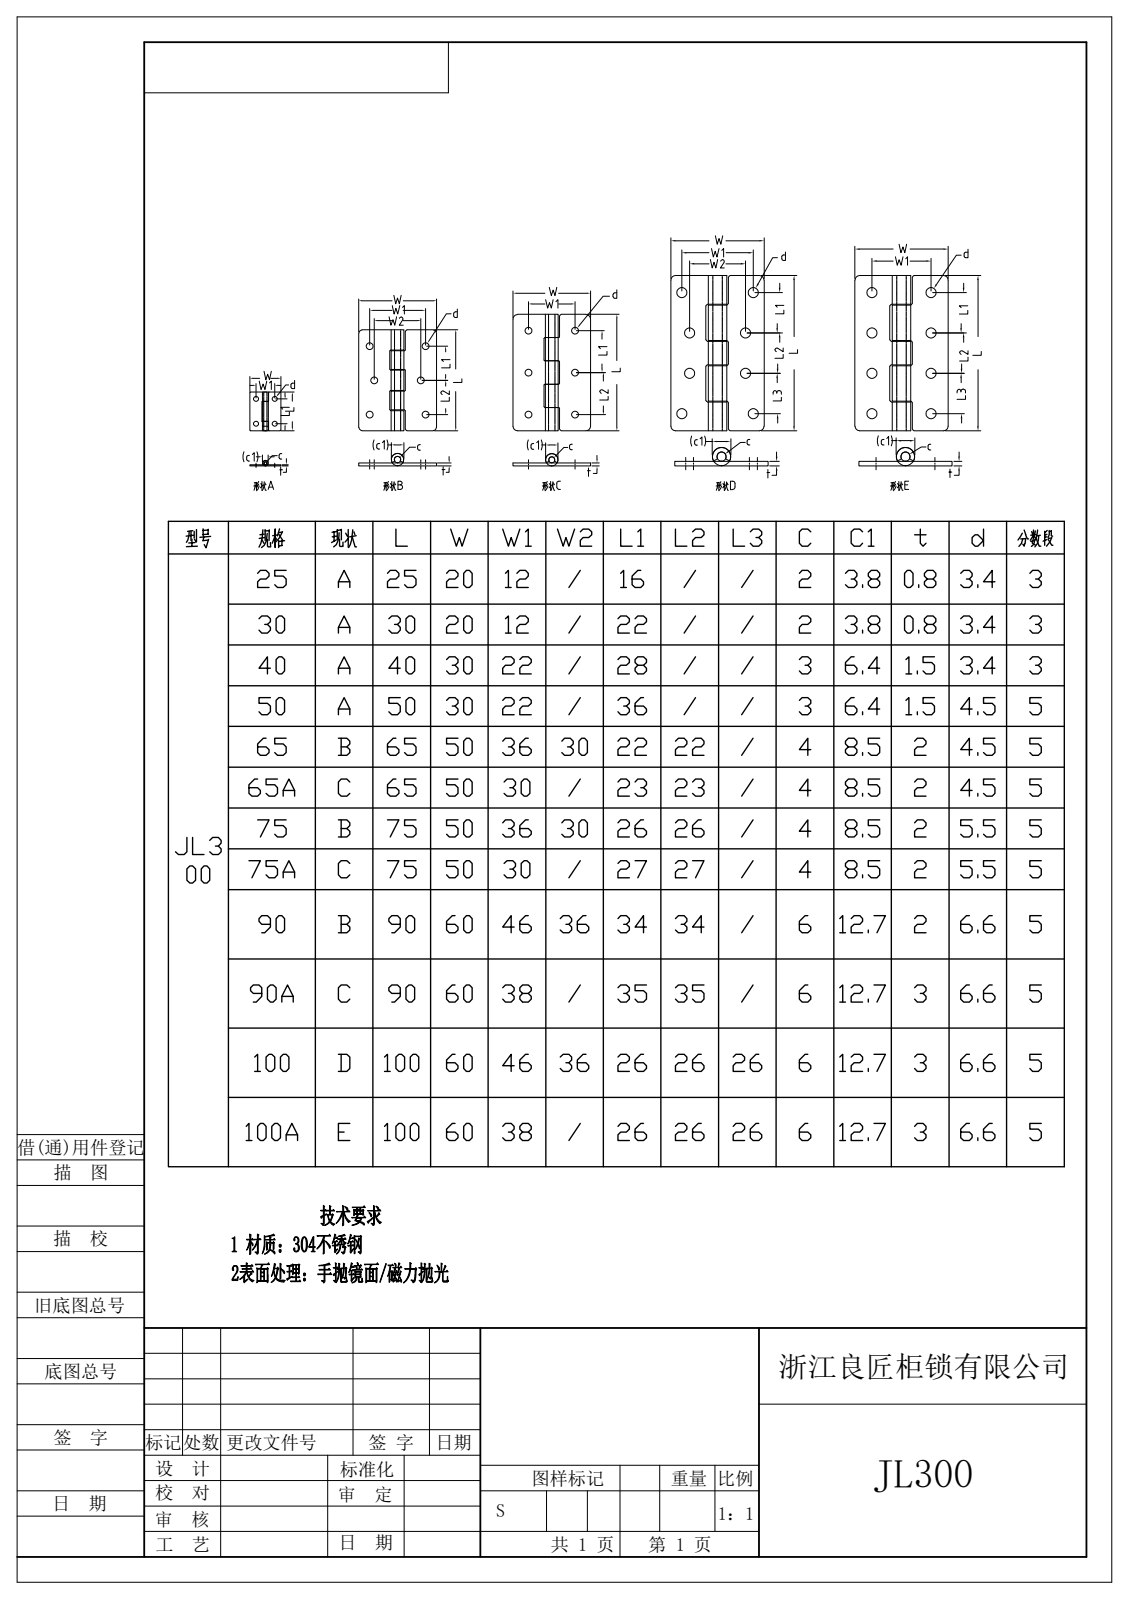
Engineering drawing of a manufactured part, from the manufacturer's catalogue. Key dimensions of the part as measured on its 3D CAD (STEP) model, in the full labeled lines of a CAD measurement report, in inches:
STEP written by: Rhino 8.5 (CONFIG_CONTROL_DESIGN)
Units: inches
Bodies: 120 solids, 1581 faces (1019 planar, 432 cylindrical, 130 other)
Overall size (bounding box): 23.328 × 6.703 × 0.676
Volume: 8.508 in³ · Surface area: 207.2 in²
Round holes (diameter × count): ⌀0.26 ×28, ⌀0.177 ×16, ⌀0.134 ×12, ⌀0.217 ×12, ⌀0.236 ×4, ⌀0.157 ×3, ⌀0.079 ×2, ⌀0.118 ×2, ⌀0.165 ×1
Round bosses / shafts (diameter × count): ⌀0.472 ×4, ⌀0.315 ×3, ⌀0.236 ×2, ⌀0.142 ×2, ⌀0.323 ×1
Partial cylindrical surfaces — rounded edges, fillets, slot ends (radius × count): R0.02 ×58, R0.039 ×40, R0.118 ×34, R0.059 ×6, R0.079 ×6, R0.012 ×4, R0.298 ×1, R0.345 ×1
Main face-to-face distances: 0.118, 0.013, 0.079, 0.115, 0.106, 0.02, 0.014, 0.098, 0.082, 0.036
Hole centre spacings: 1.024, 1.496, 1.813, 2.756, 1.043, 1.378, 1.476, 1.911
